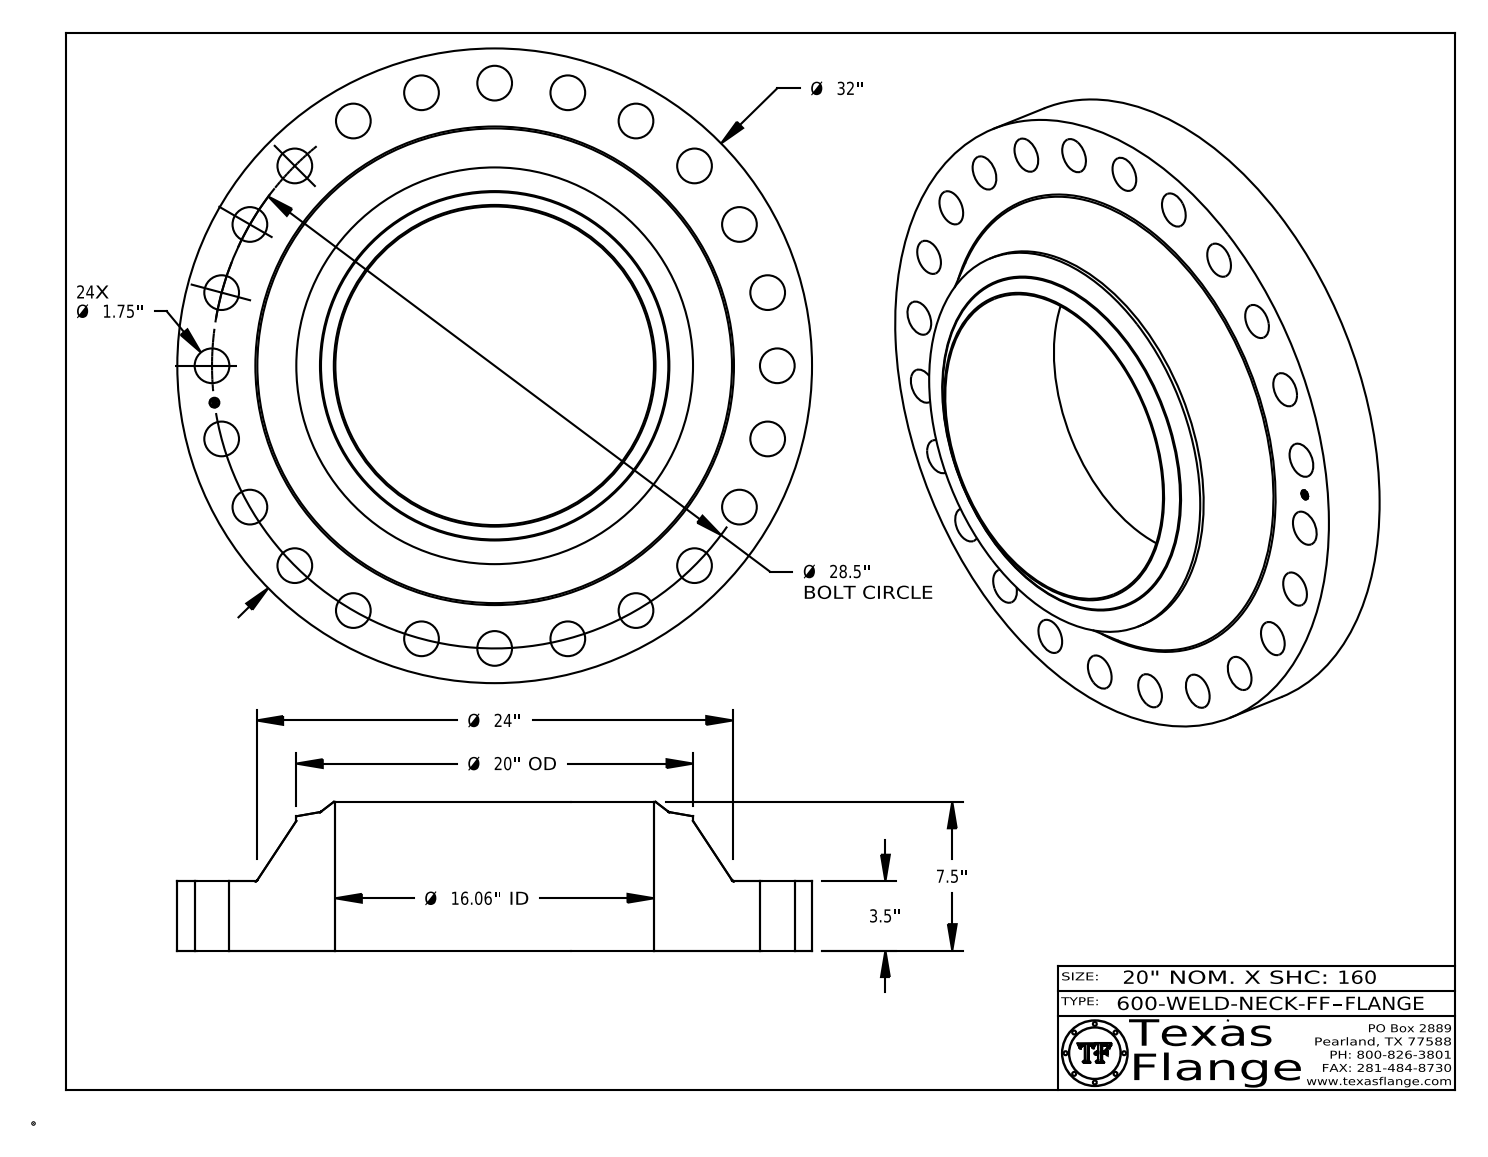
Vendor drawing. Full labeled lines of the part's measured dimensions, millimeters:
Part name (STEP PRODUCT): 600-WELD-NECK-FF
STEP written by: CATIA V5 STEP AP214 (AUTOMOTIVE_DESIGN)
Units: millimetres
Bodies: 1 solid, 452 faces (368 planar, 74 cylindrical, 10 other)
Overall size (bounding box): 812.8 × 812.8 × 190.5
Volume: 40 950 000 mm³ · Surface area: 1 559 000 mm²
Round holes (diameter × count): ⌀44.5 ×24, ⌀12.6 ×1, ⌀408 ×1
Round bosses / shafts (diameter × count): ⌀0.8 ×8, ⌀812.8 ×1, ⌀508 ×1, ⌀9.9 ×1
Main face-to-face distances: 88.9, 190.5, 101.6, 0.4, 88.5, 102, 3.8, 3.7, 0.7, 2.4
Hole centre spacings: 362, 94.5, 187.4, 626.9, 668.8, 699.2, 511.9, 277
